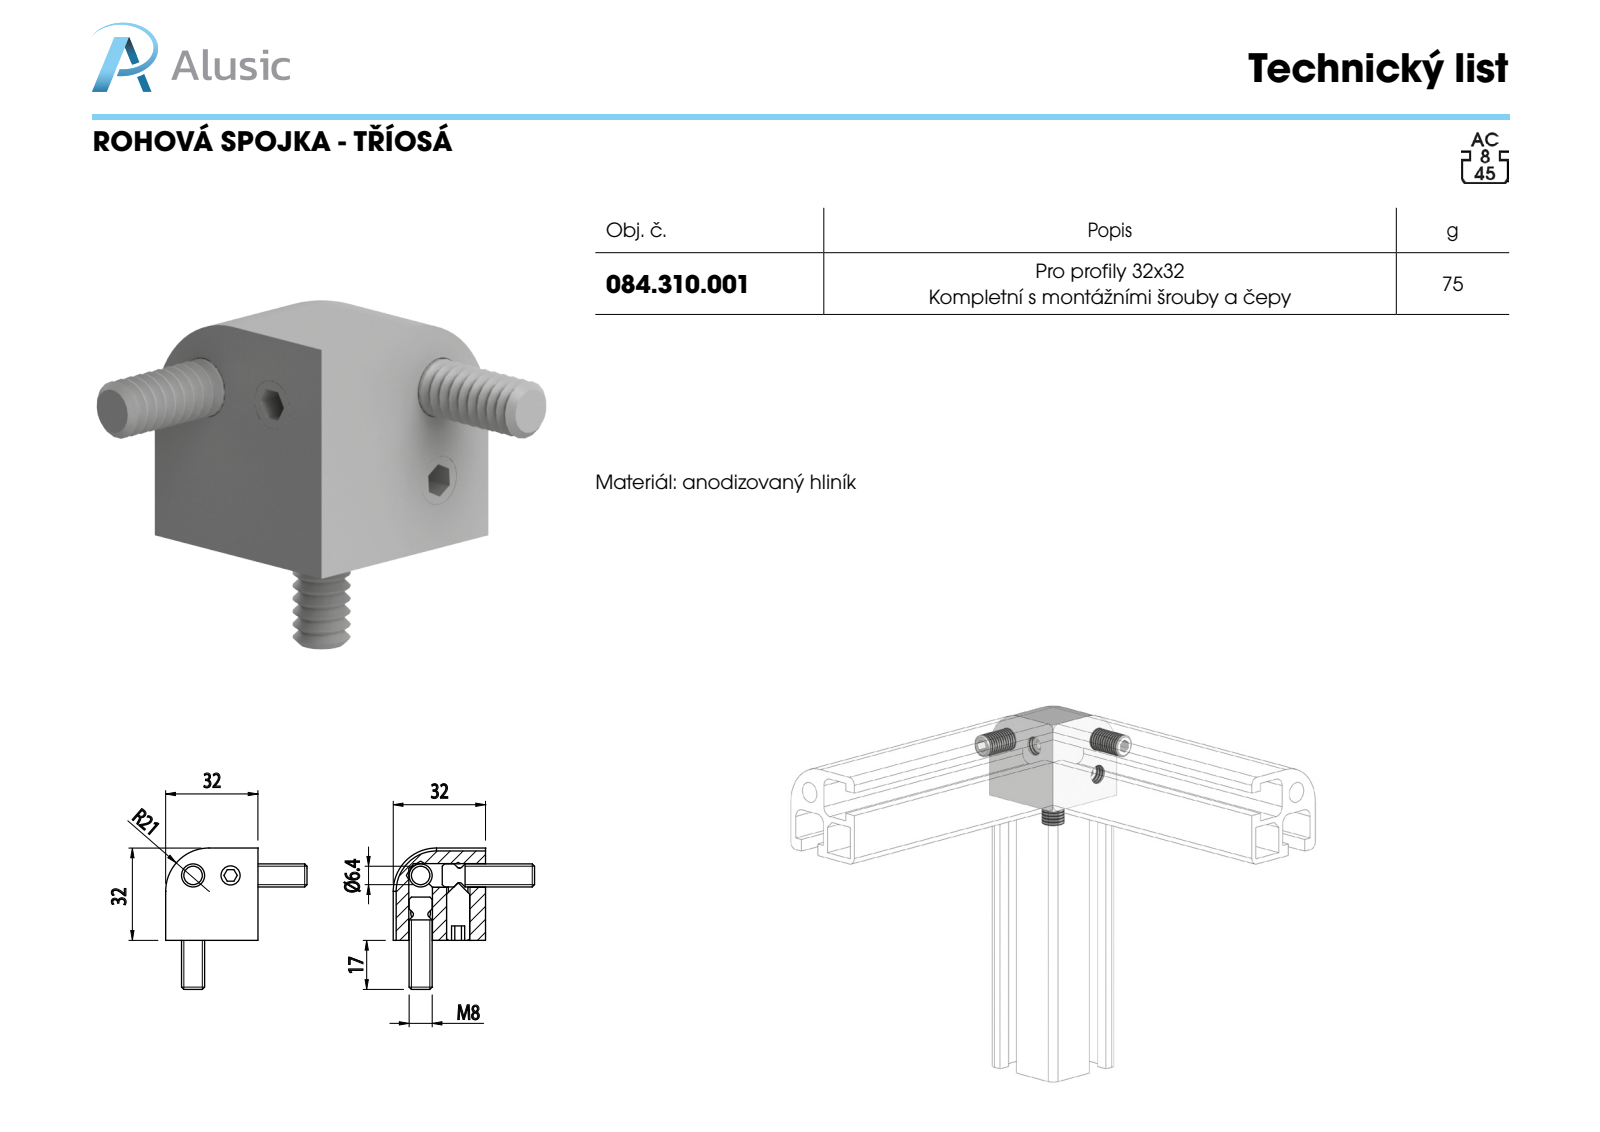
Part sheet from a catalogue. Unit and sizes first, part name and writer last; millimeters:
Units: millimetres
Overall size (bounding box): 32 × 32 × 32
Round holes (diameter × count): ⌀6.8 ×3, ⌀8.2 ×3
Partial cylindrical surfaces — rounded edges, fillets, slot ends (radius × count): R15 ×3
Main face-to-face distances: 32
Hole centre spacings: 13
Volume: 23 257 mm³ · Surface area: 7 804 mm²
Bodies: 1 solid, 70 faces (6 planar, 33 cylindrical, 31 other)
Part name (STEP PRODUCT): 084.310.001
STEP written by: SolidWorks 2011 (CONFIG_CONTROL_DESIGN)
